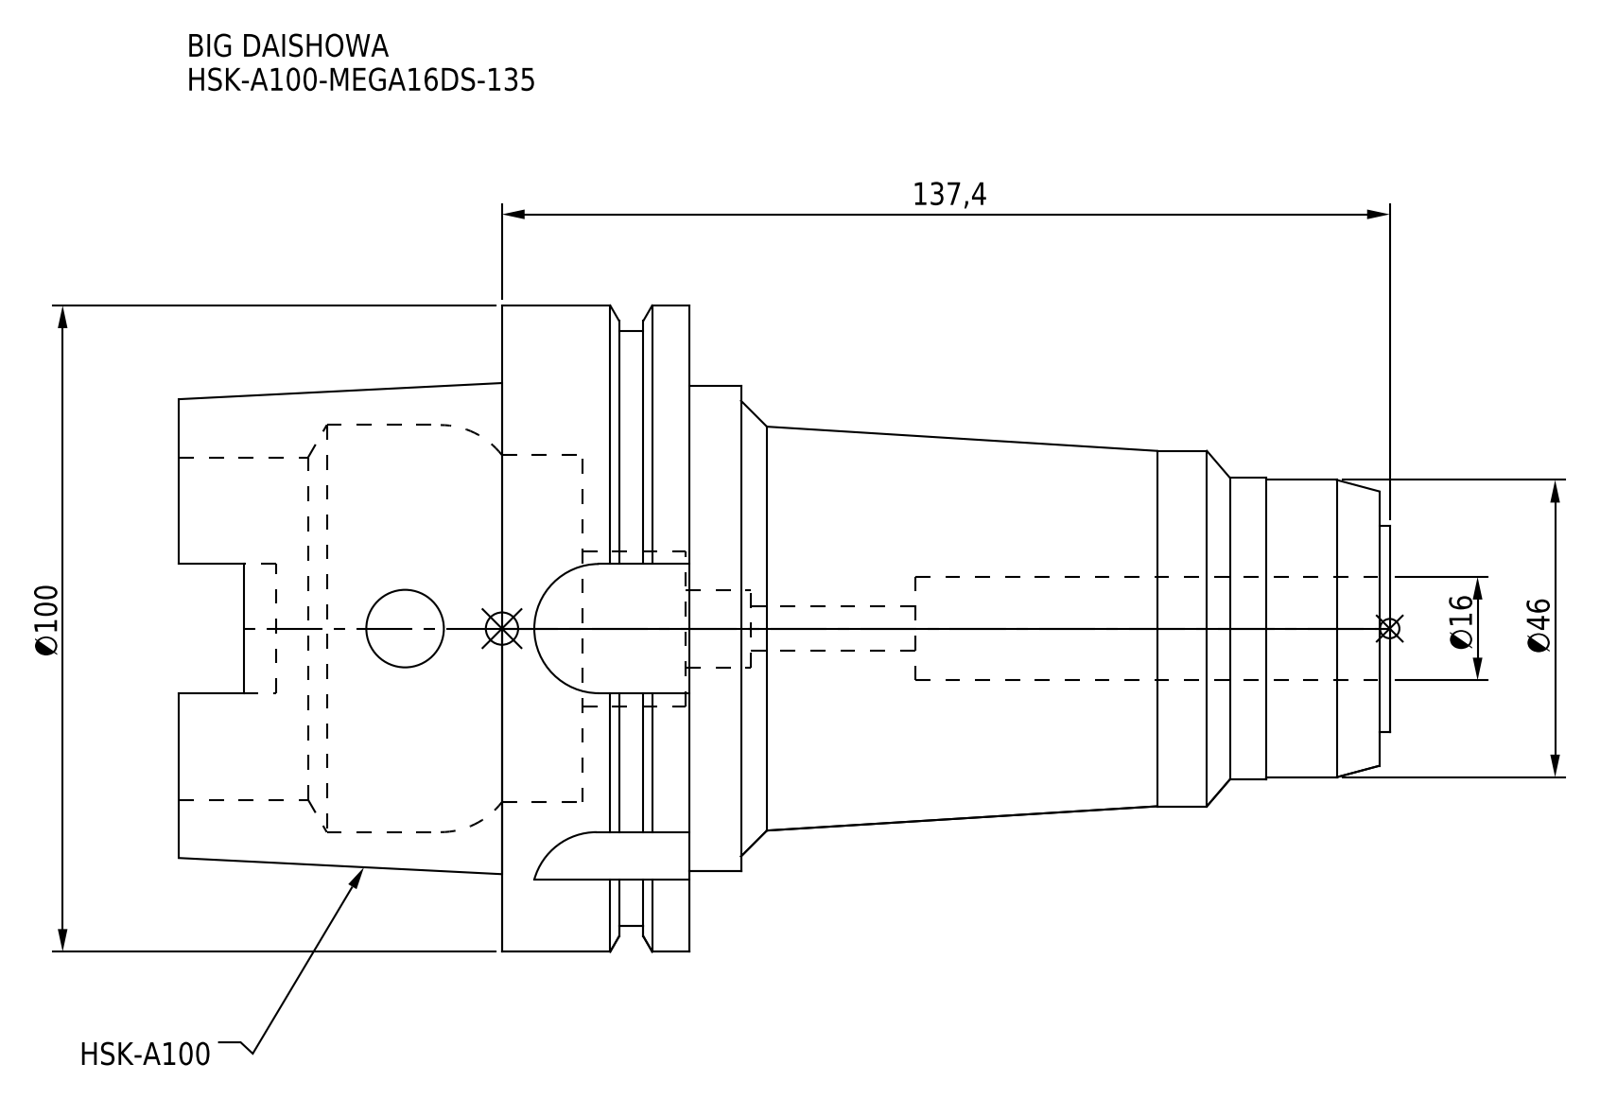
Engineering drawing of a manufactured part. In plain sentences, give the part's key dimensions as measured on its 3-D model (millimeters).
The part is named "HSK-A100-MEGA16DS-135". Its 3-D file was written by "CREO PARAMETRIC BY PTC INC, 2016380 (AUTOMOTIVE_DESIGN)". It is 1 solid with 105 faces: 37 planar, 46 cylindrical and 22 other. Overall it measures 187.4 by 100 by 100 millimeters. Its volume is 514 634 cubic millimeters and its surface area 72 051 square millimeters. Round holes: 2 of diameter 12, 1 of diameter 6.8, 1 of diameter 16, 1 of diameter 24, 1 of diameter 53, 1 of diameter 53.8, 1 of diameter 63. Round bosses or shafts: 1 of diameter 100, 1 of diameter 92, 1 of diameter 75, 1 of diameter 55, 1 of diameter 46.7, 1 of diameter 46, 1 of diameter 31.9. Partial cylindrical surfaces (rounded edges, fillets, slot ends): 4 of radius 4.88, 4 of radius 10. The main face-to-face distances are 29, 16.55, 12.45, 79, 62.45, 50, 106.8, 123.35, 135.8, 185.8.
